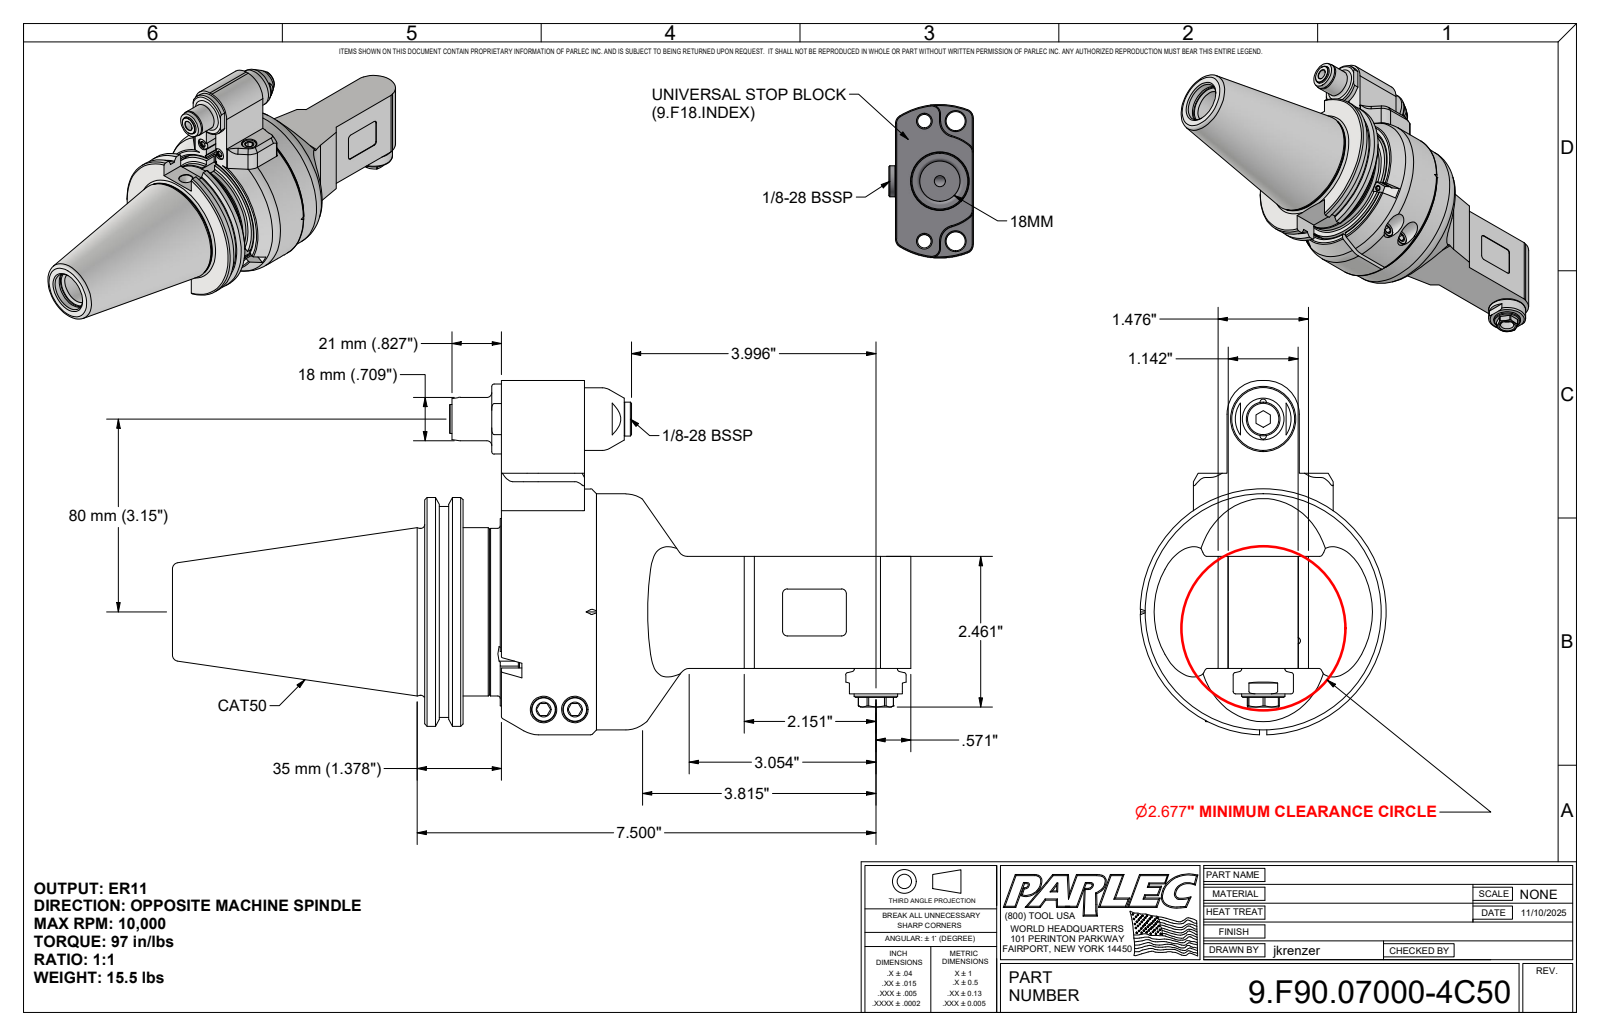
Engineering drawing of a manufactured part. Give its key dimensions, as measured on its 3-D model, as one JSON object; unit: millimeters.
{"part_name": "9.F90.07000-4C50; 9_F90_07000; 9GA11C_458", "step_written_by": "Autodesk Inventor 2025 (AUTOMOTIVE_DESIGN)", "units": "millimeters", "bodies": {"solids": 4, "faces": 570, "planar": 260, "cylindrical": 166, "other": 144}, "overall_size": [306.6, 147, 102], "volume_mm3": 1085000, "surface_area_mm2": 162200, "round_holes": [[8.5, 21], [6.5, 3], [2.6, 2], [3.3, 2], [4.2, 2], [5, 2], [8, 2], [10.4, 2], [11, 2], [12.5, 2], [2.5, 1], [3, 1]], "round_bosses_or_shafts": [[10, 4], [18, 3], [12, 2], [8, 2], [6, 2], [2.5, 2], [102, 1], [98.4, 1]], "partial_cylinders_radius": [[1, 14], [2, 12], [3, 6], [4, 4], [0.5, 2], [8, 2], [14, 2], [14.5, 2]], "face_to_face_distances": [0.5, 32.5, 32, 55.4, 23.4, 23, 46.5, 71.3, 39.3, 38.8], "hole_center_spacings": [38.5, 37.3, 46.3, 54.5, 76.3, 10.7, 67.3, 74]}
